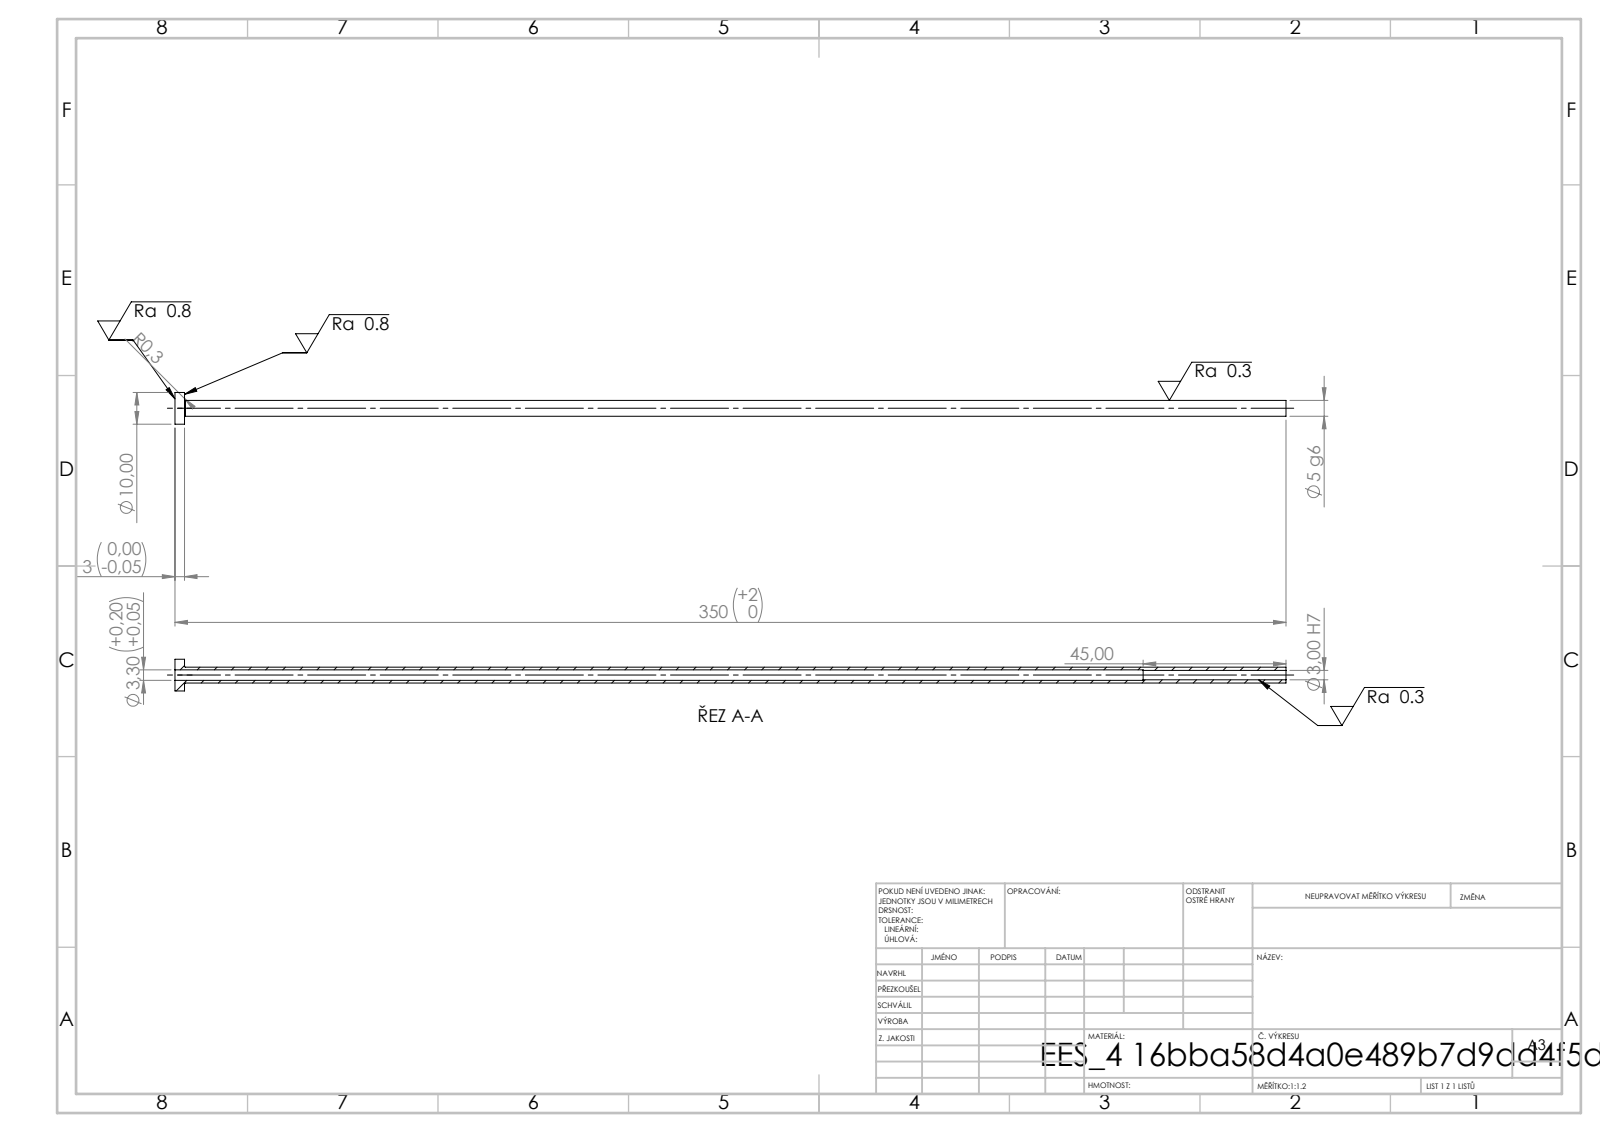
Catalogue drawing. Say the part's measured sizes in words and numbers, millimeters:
Its 3-D file was written by "SolidWorks 2019 (CONFIG_CONTROL_DESIGN)". It is 1 solid with 14 faces: 4 planar, 8 cylindrical and 2 other. Overall it measures 350 by 10 by 10 millimeters. Its volume is 4 123 cubic millimeters and its surface area 9 272 square millimeters. Round holes: 1 of diameter 3, 1 of diameter 3.3. Round bosses or shafts: 1 of diameter 10, 1 of diameter 5. The main face-to-face distances are 3, 350, 347, 305, 302, 45.
